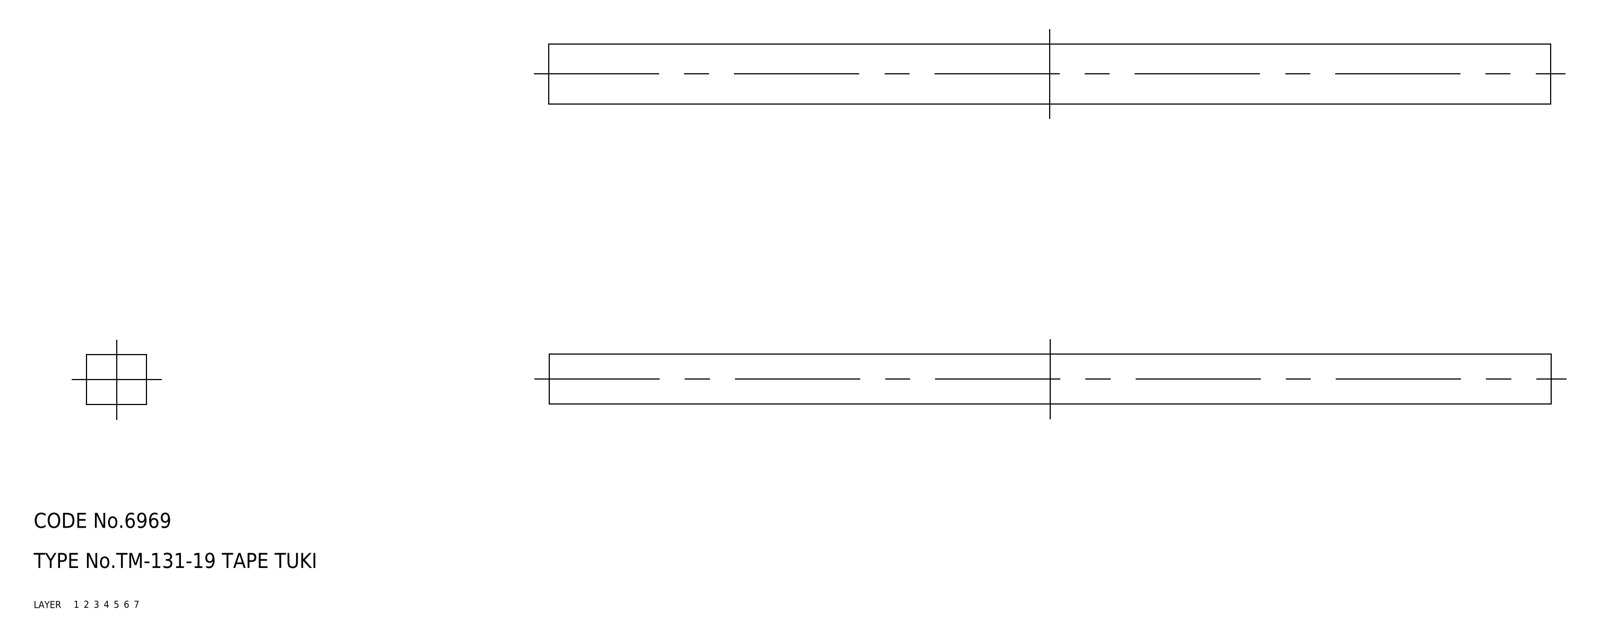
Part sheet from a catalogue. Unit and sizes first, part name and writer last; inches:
Units: inches
Overall size (bounding box): 7.874 × 0.472 × 0.394
Volume: 1.465 in³ · Surface area: 14.01 in²
Bodies: 1 solid, 6 faces (0 planar, 0 cylindrical, 6 other)
Part name (STEP PRODUCT): rubber foam
STEP written by: CADfix (AUTOMOTIVE_DESIGN)
